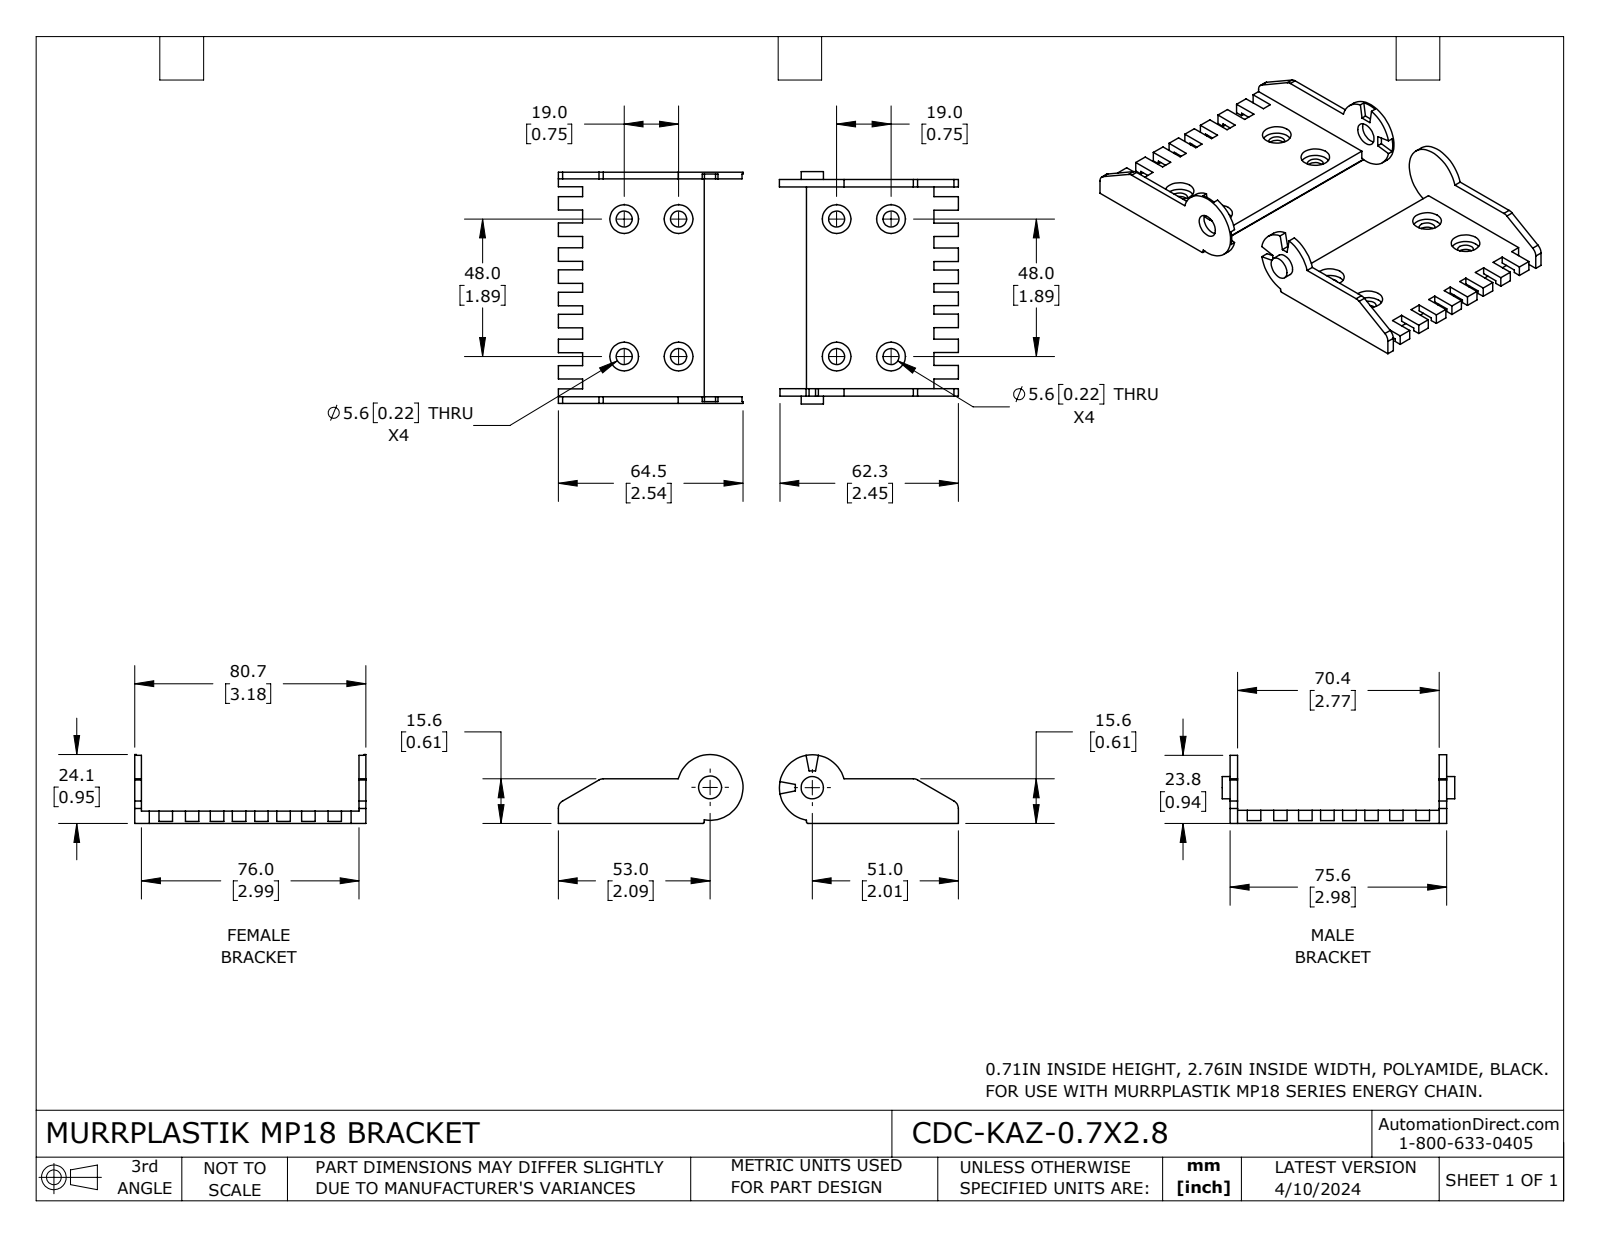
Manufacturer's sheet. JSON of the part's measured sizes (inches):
{"part_name": "CDC-KAZ-0.7X2.8; CDC-KAZ-0.7X2.8_Male; CDC-KAZ-0.7X2.8_Female", "step_written_by": "SolidWorks 2023 (CONFIG_CONTROL_DESIGN)", "units": "inches", "bodies": {"solids": 2, "faces": 215, "planar": 158, "cylindrical": 57, "other": 0}, "overall_size": [5.5, 3.197, 0.949], "volume_in3": 2.325, "surface_area_in2": 40.1, "round_holes": [[0.22, 8], [0.394, 8], [0.315, 1]], "round_bosses_or_shafts": [[0.307, 1]], "partial_cylinders_radius": [[0.118, 4], [0.02, 2], [0.453, 2]], "face_to_face_distances": [0.169, 0.181, 0.11, 0.1, 3.077, 0.102, 0.203, 2.974, 2.874, 2.984], "hole_center_spacings": [0.748, 1.89, 2.032, 2.921, 3.479, 2.173, 2.88, 3.669]}
